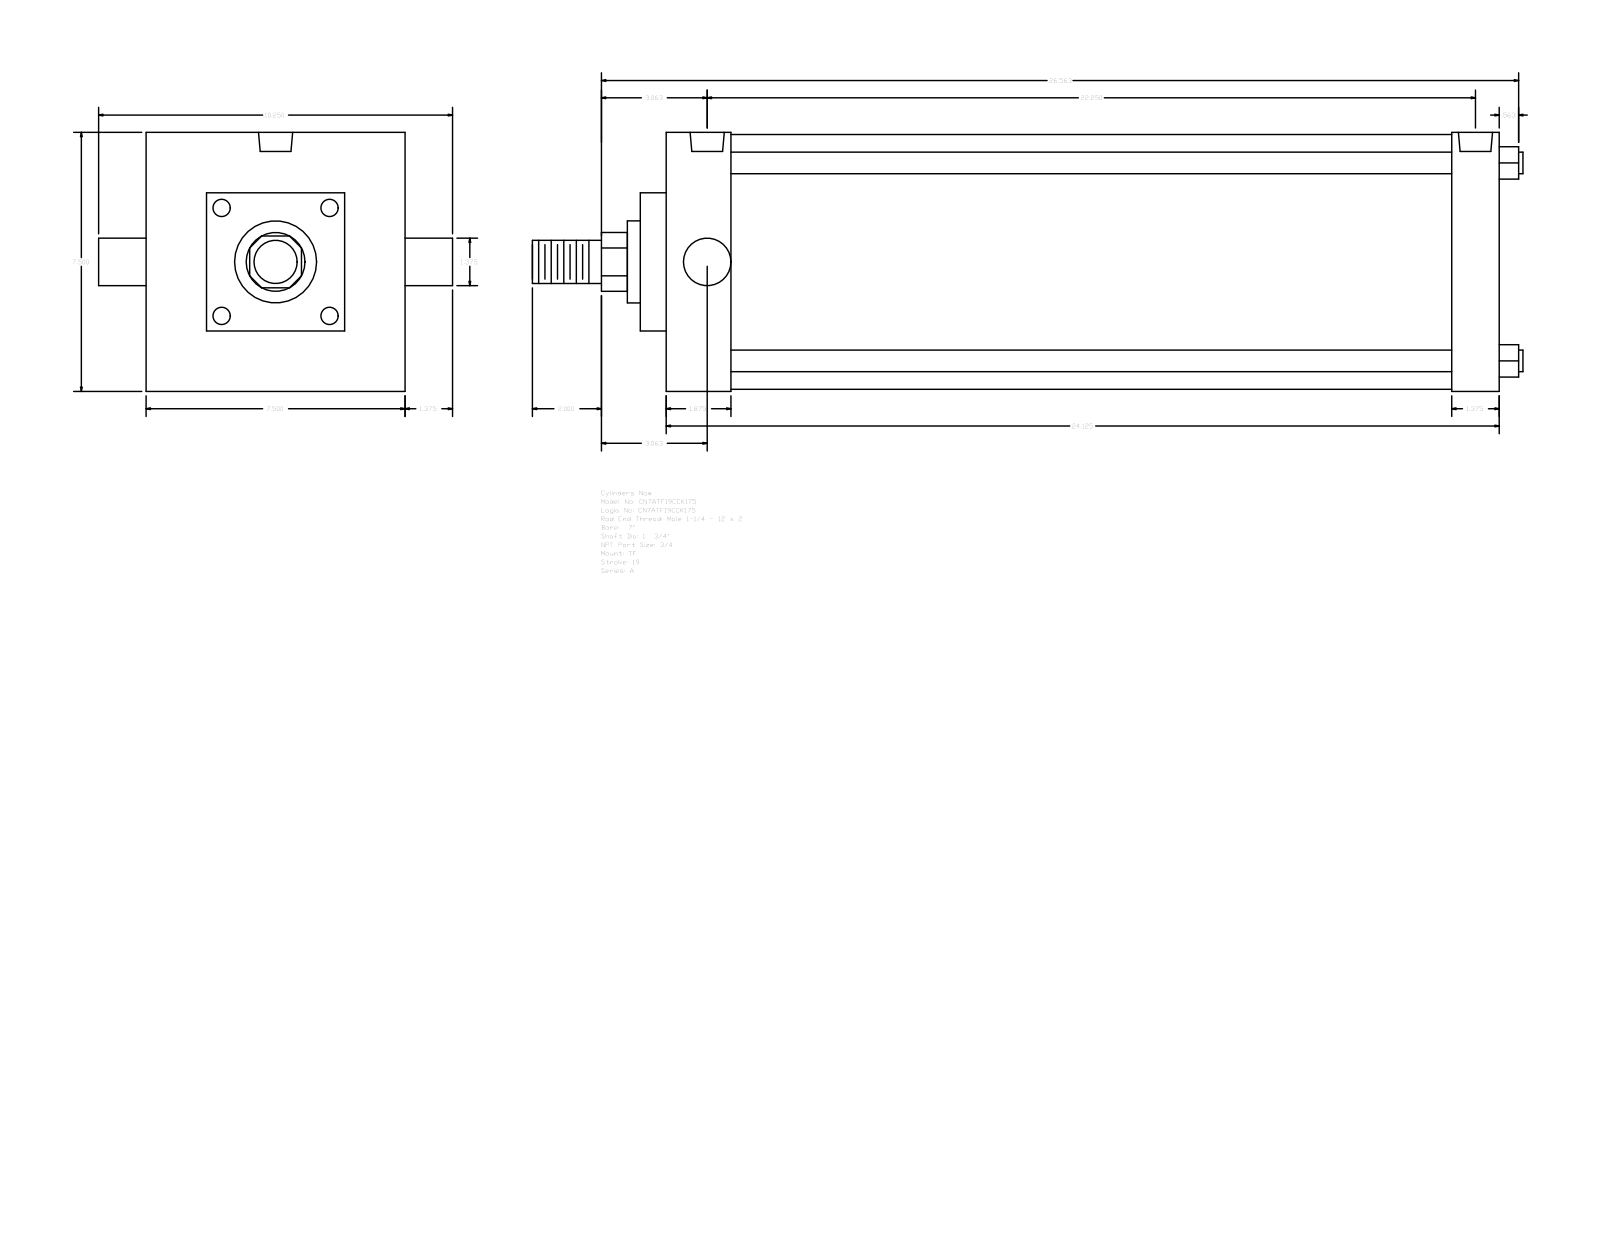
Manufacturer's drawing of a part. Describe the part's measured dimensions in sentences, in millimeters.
The part is named "A_TF__0700_1.75". Its 3-D file was written by "GSSL Pune (CONFIG_CONTROL_DESIGN)". It is 0 solids with 89 faces: 65 planar, 24 cylindrical and 0 other. Overall it measures 728.66 by 260.35 by 190.5 millimeters. Round holes: 3 of diameter 15.08, 2 of diameter 25.12. Round bosses or shafts: 4 of diameter 15.88, 1 of diameter 187.32, 1 of diameter 60.33, 1 of diameter 44.45, 1 of diameter 34.92, 1 of diameter 31.75. Partial cylindrical surfaces (rounded edges, fillets, slot ends): 1 of radius 21.63. The main face-to-face distances are 190.5, 612.78, 146.05, 19.05, 47.63, 565.15, 577.86, 530.23, 34.92, 44.45. The hole center spacings are 5.56, 559.59, 554.03, 565.15.
